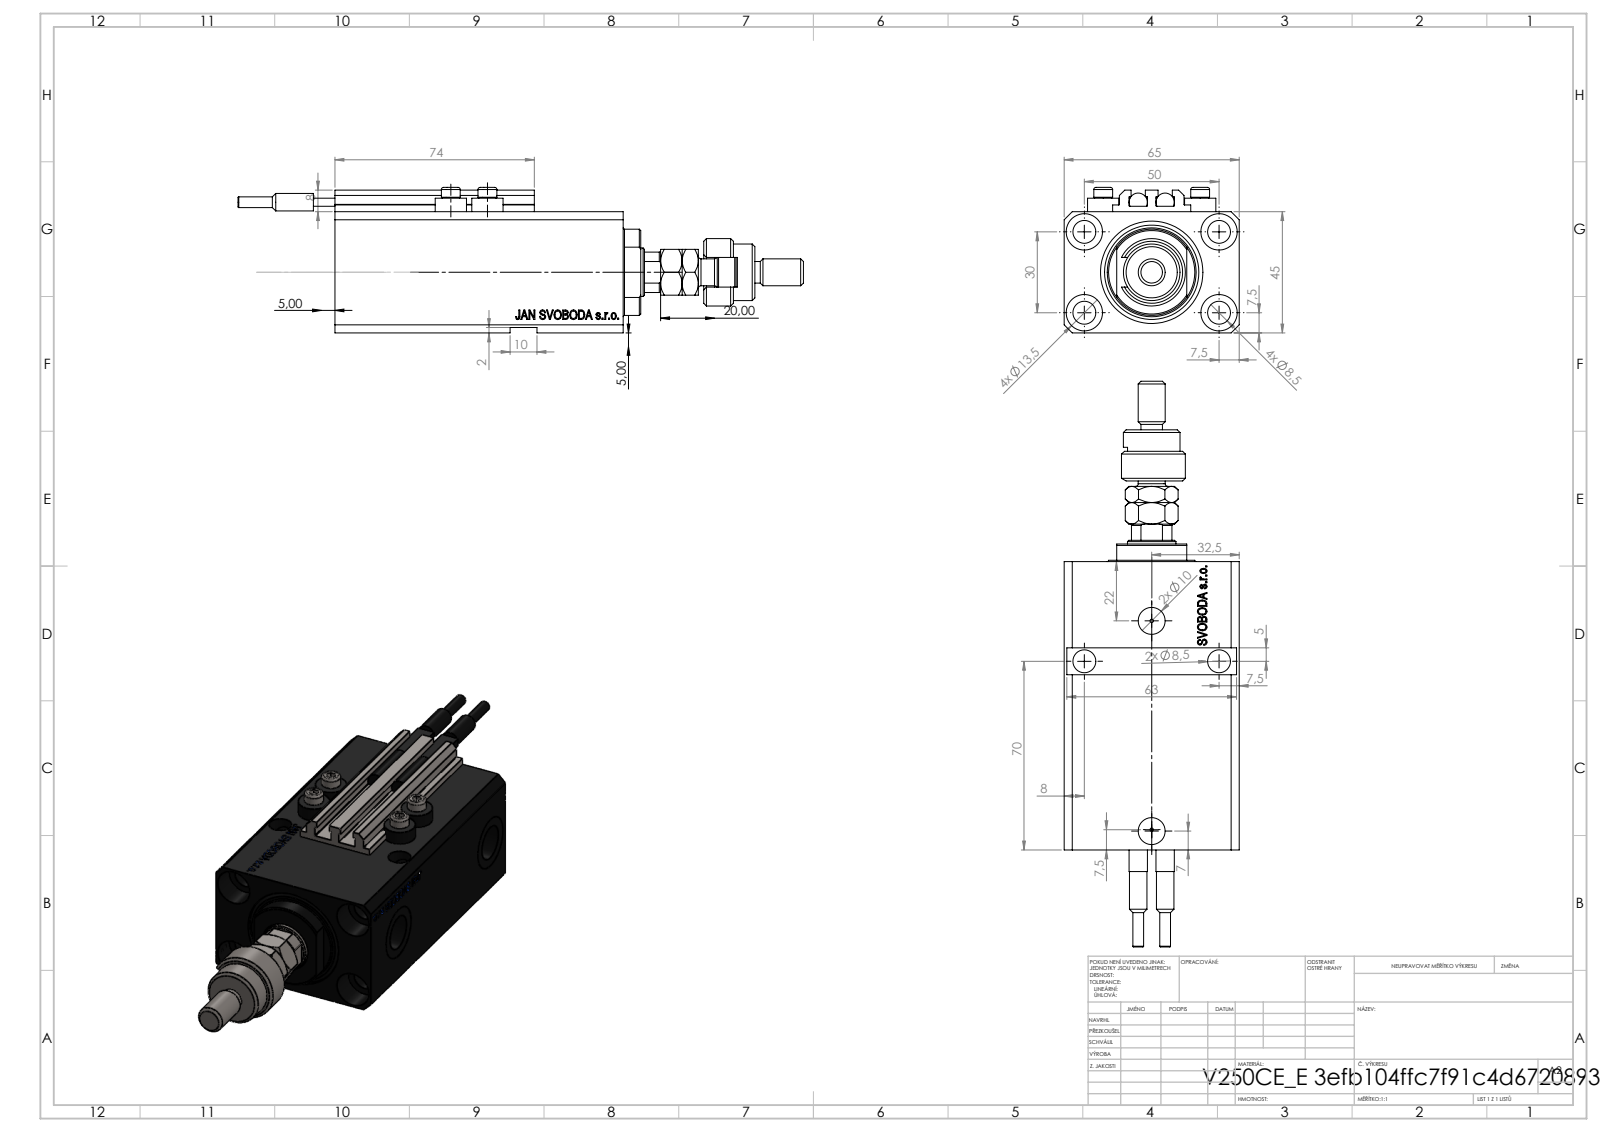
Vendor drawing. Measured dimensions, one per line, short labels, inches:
name: V250CE_C_VCP; FEMALE_PART_FOR_DFA; MFA; SWITCH_V250CE (+3 more)
written by: SolidWorks 2019 (CONFIG_CONTROL_DESIGN)
unit: in
bodies: 12 solids, 1224 faces (571 planar, 171 cylindrical, 482 other)
size: 8.268 × 2.559 × 2.126
volume: 17.62 in³; area: 131.9 in²
holes: 9× ⌀0.335, 4× ⌀0.049, 4× ⌀0.157, 4× ⌀0.531, 2× ⌀0.394, 2× ⌀0.518, 2× ⌀0.787, 1× ⌀0.709, 1× ⌀1.496
bosses: 4× ⌀0.457, 4× ⌀0.276, 2× ⌀0.268, 2× ⌀0.256, 2× ⌀0.157, 1× ⌀0.984, 1× ⌀0.827, 1× ⌀0.63
rounds: 10× R0.008, 1× R0.217, 1× R0.335, 1× R0.344, 1× R0.63
face distances: 1.772, 2.559, 0.551, 0.079, 1.85, 0.118, 3.661, 4.213, 0.197, 0.394
hole spacings: 1.148, 1.969, 0.535, 0.581, 0.595, 1.083, 1.098, 1.181
